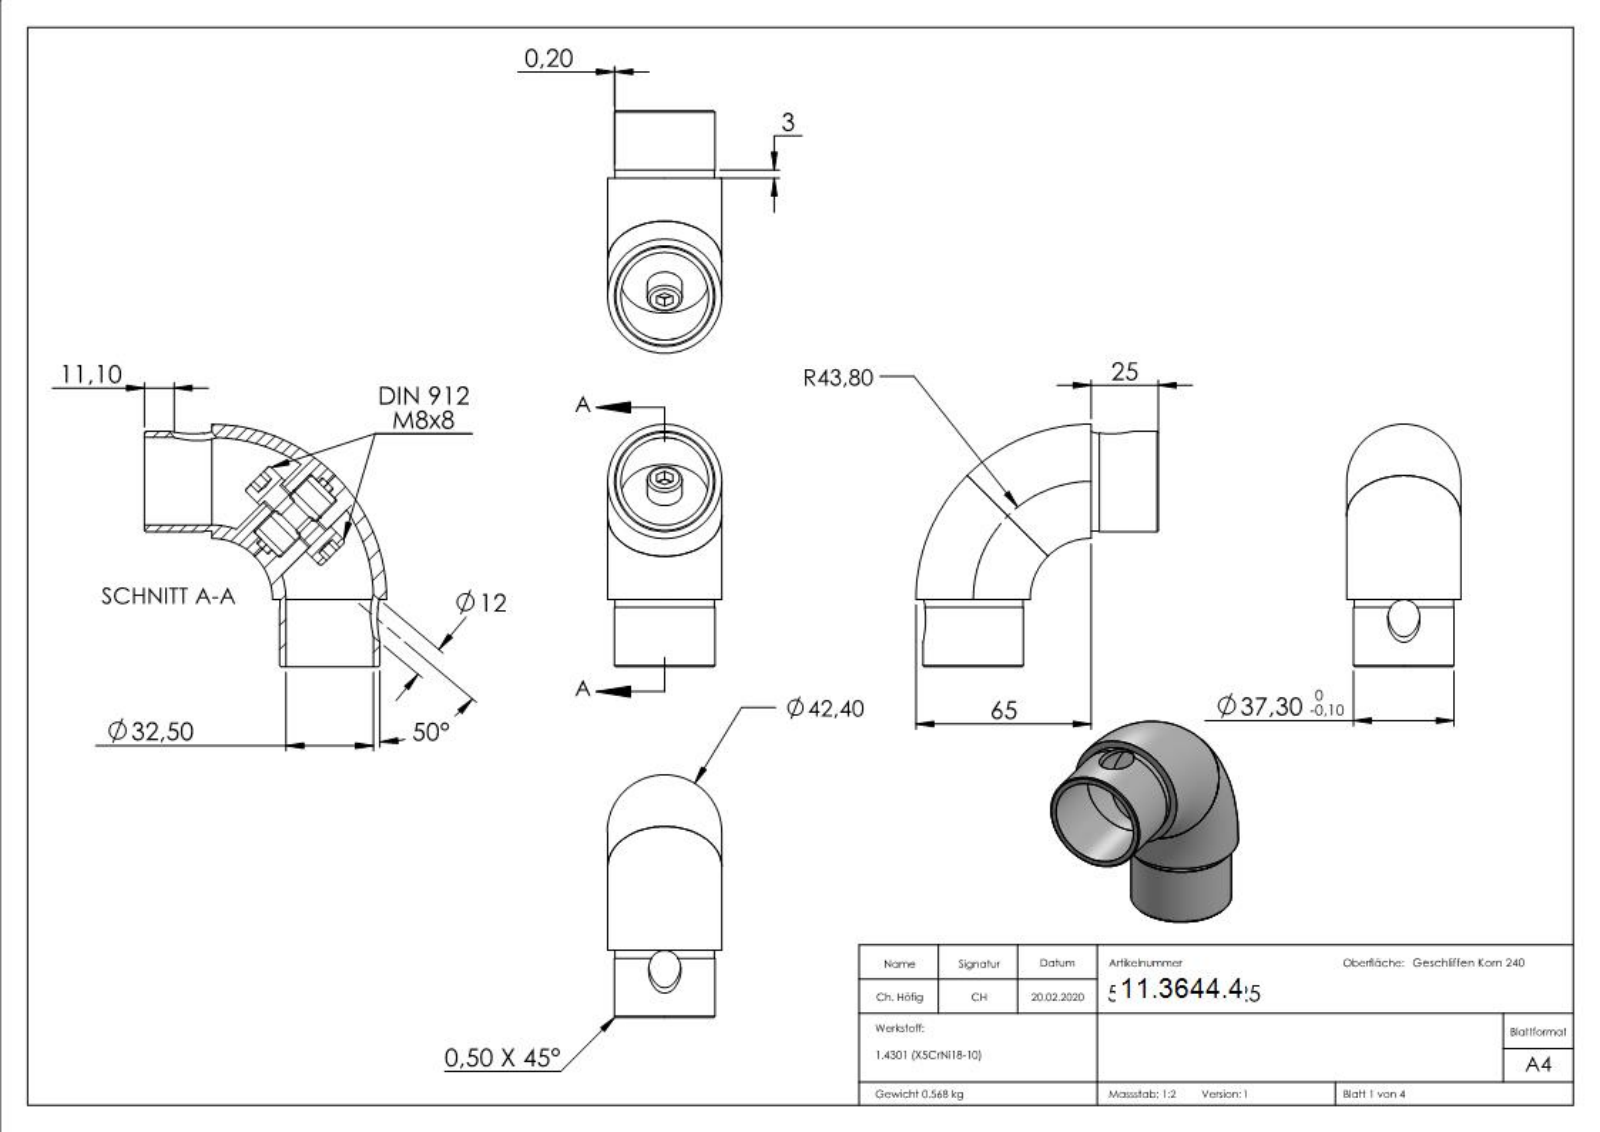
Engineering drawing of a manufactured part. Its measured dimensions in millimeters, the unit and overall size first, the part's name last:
Units: millimetres
Overall size (bounding box): 13955.19 × 12419.37 × 10009.53
Round holes (diameter × count): ⌀9.5 ×2, ⌀12 ×2, ⌀30 ×2, ⌀32.5 ×2, ⌀34.4 ×2, ⌀6.8 ×1
Round bosses / shafts (diameter × count): ⌀37.3 ×2, ⌀36.9 ×2, ⌀13 ×2, ⌀8 ×2
Main face-to-face distances: 6.5, 0.5, 7, 13.5, 23.89, 11.95, 11.94, 18.45, 5.44, 5.45
Volume: 71 873 mm³ · Surface area: 35 853 mm²
Bodies: 5 solids, 610 faces (318 planar, 20 cylindrical, 272 other)
Part name (STEP PRODUCT): 5616X-320V Teil2; 56160-320V-25; DIN 912 Konfig_DIN 912 M8x8; 5616X-320V Teil1_56160-320V-25 Teil1 (+3 more)
STEP written by: SolidWorks 2015 (CONFIG_CONTROL_DESIGN)
